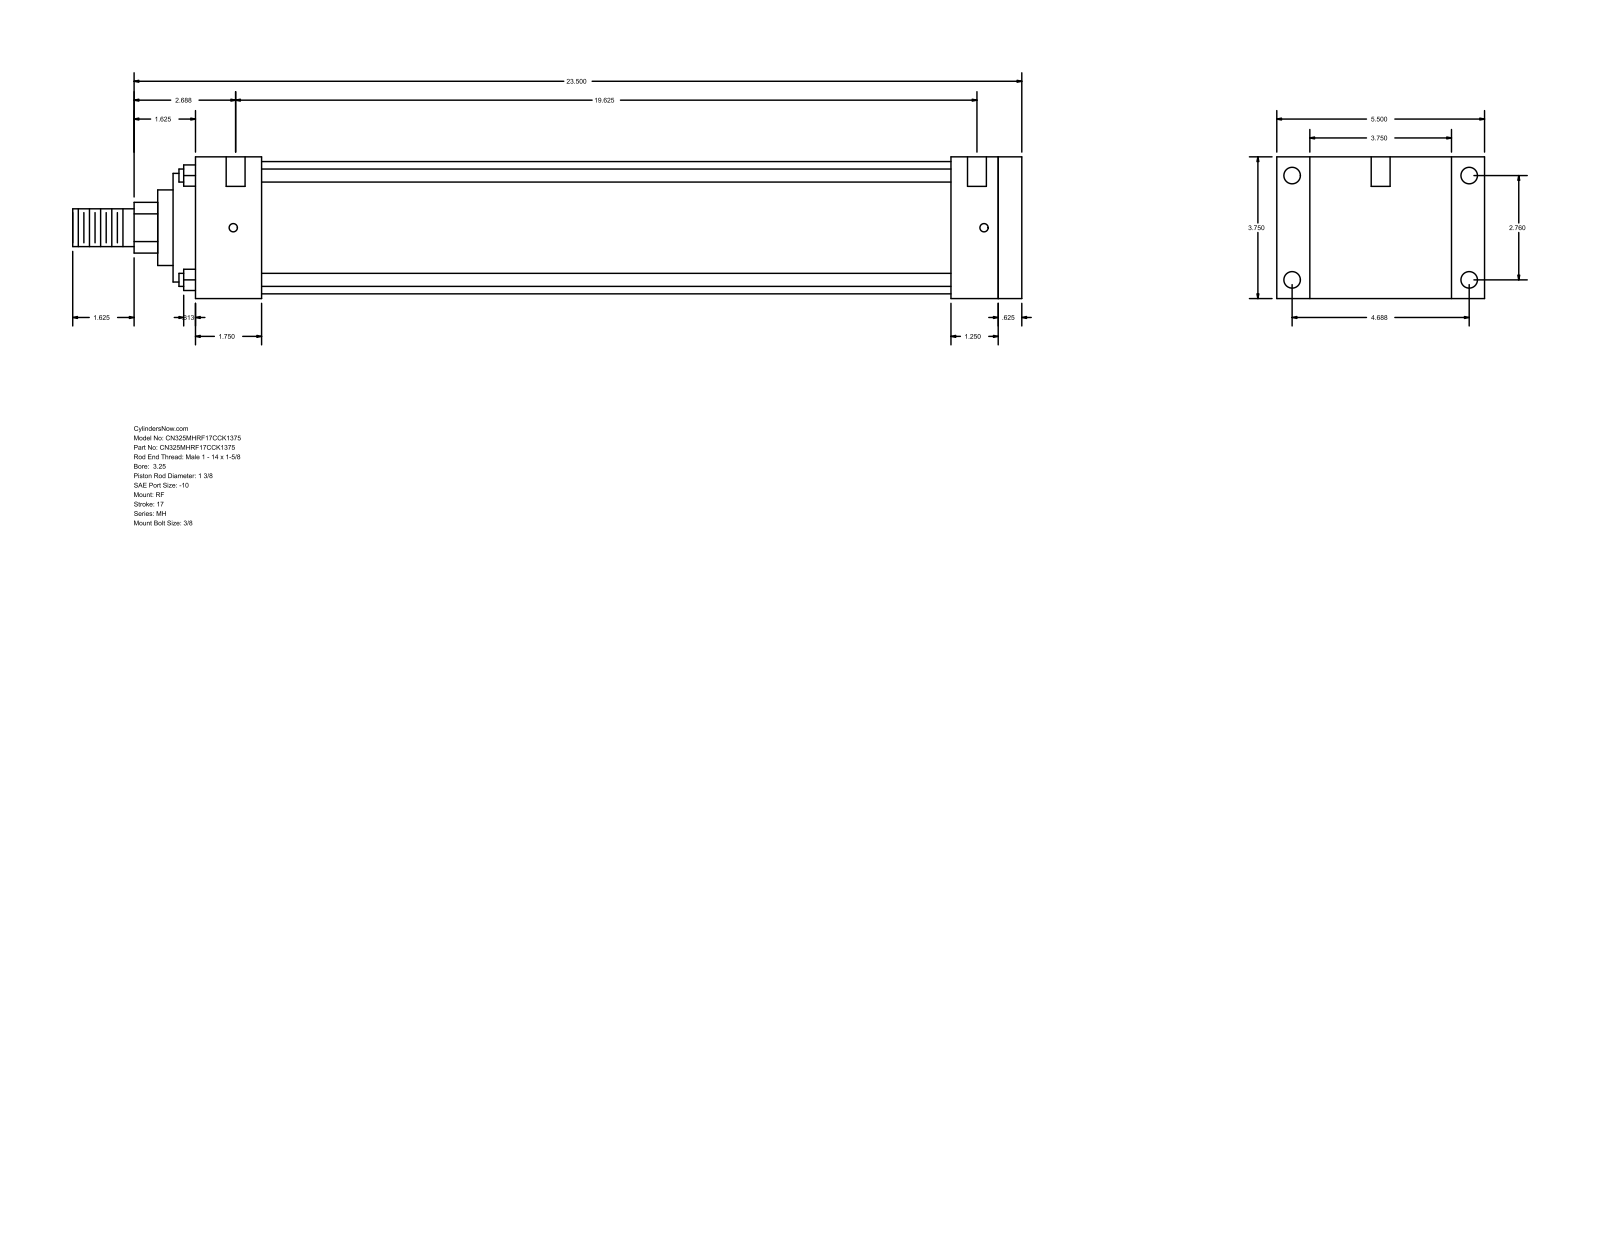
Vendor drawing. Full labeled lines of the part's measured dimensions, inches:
Part name (STEP PRODUCT): MH_RF__0325_1.375
STEP written by: GSSL Pune (CONFIG_CONTROL_DESIGN)
Units: inches
Bodies: 0 solids, 94 faces (65 planar, 29 cylindrical, 0 other)
Overall size (bounding box): 25.125 × 5.5 × 3.75
Round holes (diameter × count): ⌀0.219 ×4, ⌀0.438 ×4, ⌀0.5 ×2
Round bosses / shafts (diameter × count): ⌀0.345 ×4, ⌀3.5 ×1, ⌀2.875 ×1, ⌀2 ×1, ⌀1.375 ×1, ⌀1 ×1
Partial cylindrical surfaces — rounded edges, fillets, slot ends (radius × count): R0.672 ×1
Main face-to-face distances: 3.75, 21.875, 0.625, 21.25, 0.875, 4.625, 1.75, 19.5, 20.125, 20
Hole centre spacings: 2.76, 4.687, 5.439, 19.875, 0.063, 0.187, 19.625, 19.688
